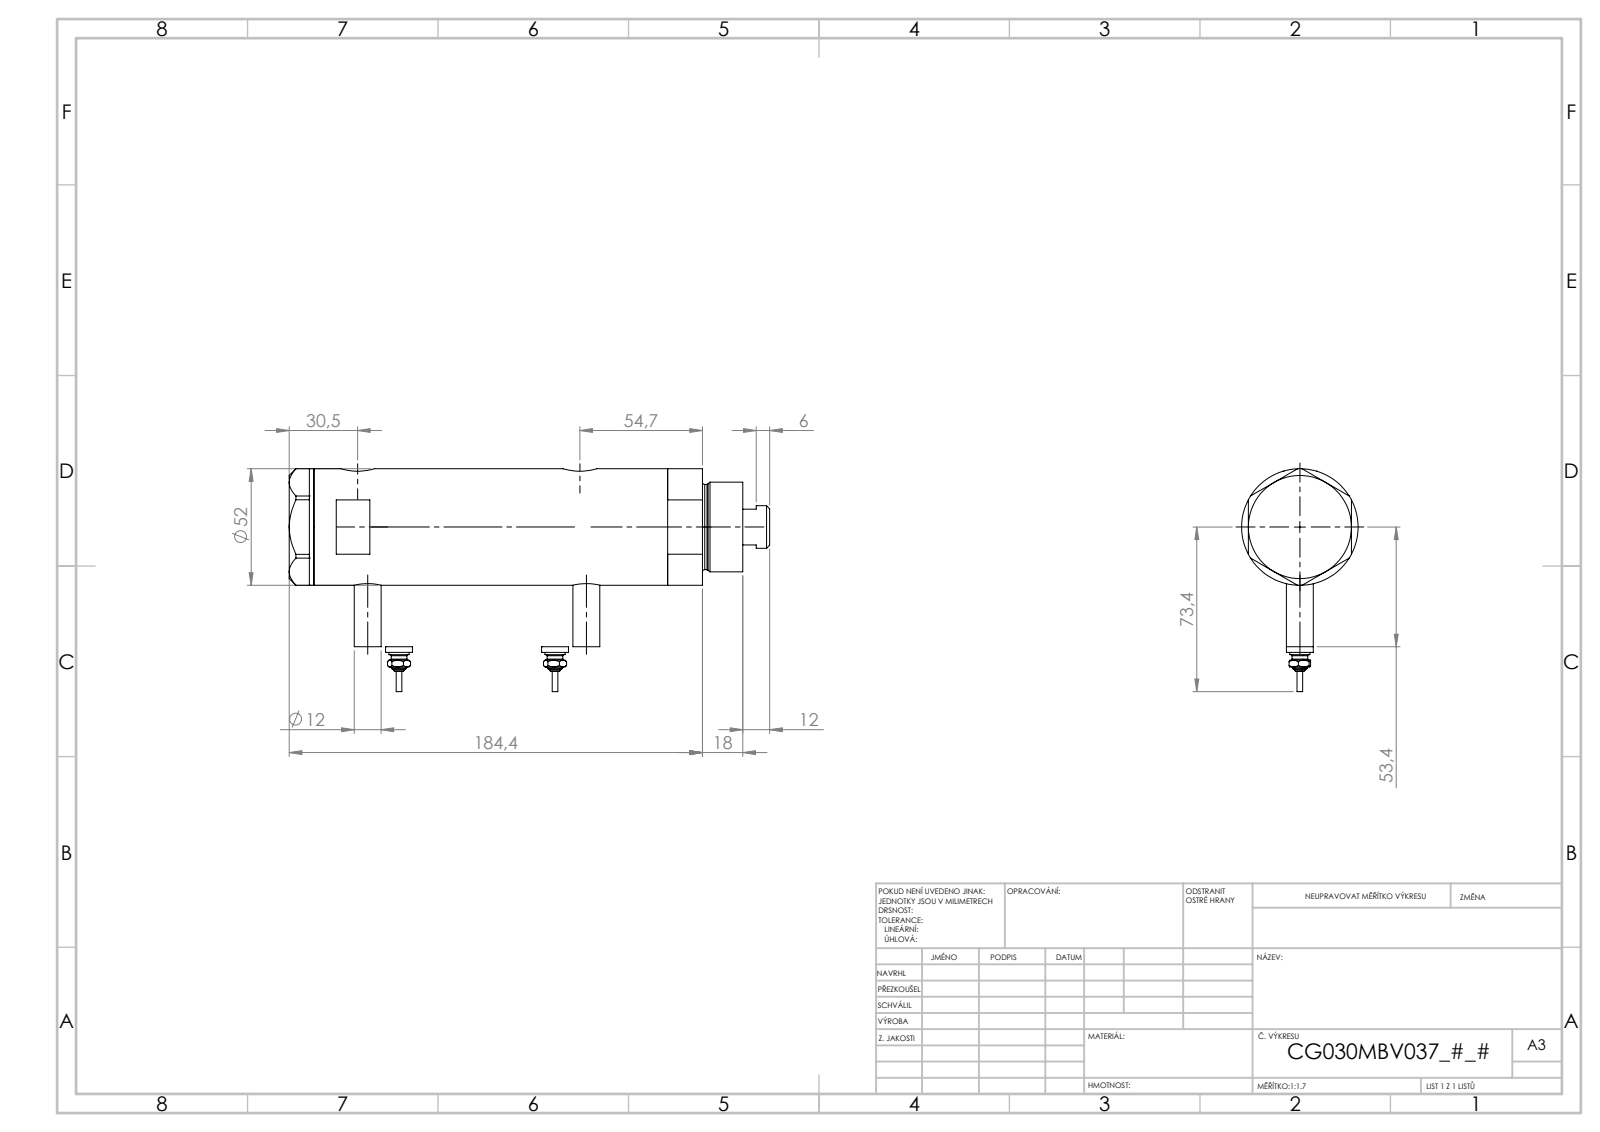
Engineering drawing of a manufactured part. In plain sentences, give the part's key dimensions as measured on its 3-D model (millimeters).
The part is named "V270CG_MIDDLE; V270CG_BACK; V270CG_SWITCH; V270CG_VC (+1 more)". Its 3-D file was written by "SolidWorks 2019 (CONFIG_CONTROL_DESIGN)". It is 6 solids with 246 faces: 95 planar, 77 cylindrical and 74 other. Overall it measures 186.02 by 84.3 by 52 millimeters. Its volume is 334 423 cubic millimeters and its surface area 78 893 square millimeters. Round holes: 2 of diameter 5, 2 of diameter 9.73, 2 of diameter 12.5, 2 of diameter 15, 1 of diameter 6.5, 1 of diameter 20, 1 of diameter 21.5, 1 of diameter 30, 1 of diameter 33, 1 of diameter 44. Round bosses or shafts: 3 of diameter 12, 2 of diameter 9, 2 of diameter 7, 2 of diameter 4.34, 2 of diameter 2.4, 1 of diameter 52, 1 of diameter 40, 1 of diameter 38. The main face-to-face distances are 90.56, 23.8, 66.76, 11, 34.8, 101.56, 46, 137.96, 126.96, 103.16. The hole center spacings are 2.9, 4.5, 63.75, 66.65, 68.25, 71.15, 2.89, 2.91.
